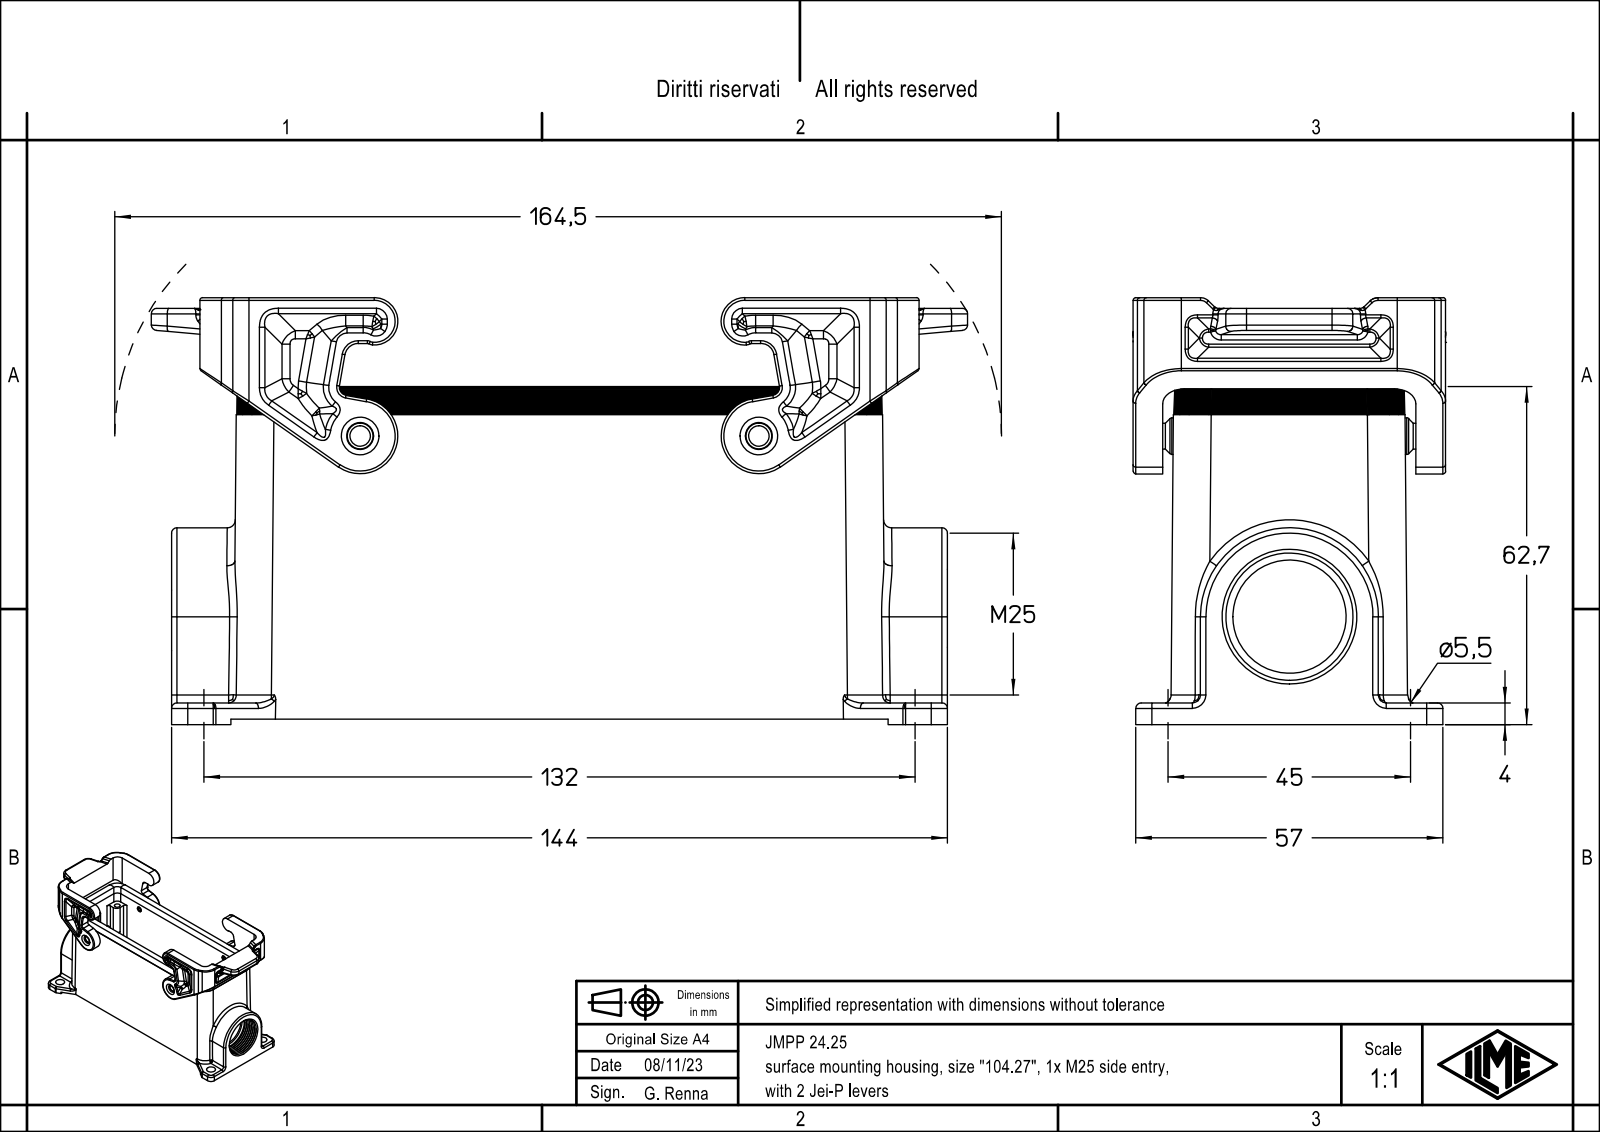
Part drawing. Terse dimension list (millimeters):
name: JMPP 24.25
written by: Creo Elements/Direct Modeling 20.1B 02-Apr-2019 (C) Parametric Technology GmbH (AUTOMOTIVE_DESIGN)
unit: mm
bodies: 1 solid, 893 faces (171 planar, 314 cylindrical, 408 other)
size: 151.5 × 79.2 × 58.08
volume: 143 696 mm³; area: 66 199 mm²
holes: 4× ⌀3, 4× ⌀3.5, 4× ⌀5.5, 2× ⌀4.8, 1× ⌀21, 1× ⌀23.6
bosses: 2× ⌀6.8
rounds: 50× R0.5, 48× R1, 38× R3, 24× R2, 16× R1.5, 12× R4, 12× R6, 10× R7
face distances: 3, 47, 7, 1, 4, 10.25, 133.75, 38.9, 5.5, 52.5
hole spacings: 16.64, 38.63, 118.34, 123.37, 27, 45, 104, 107.45
